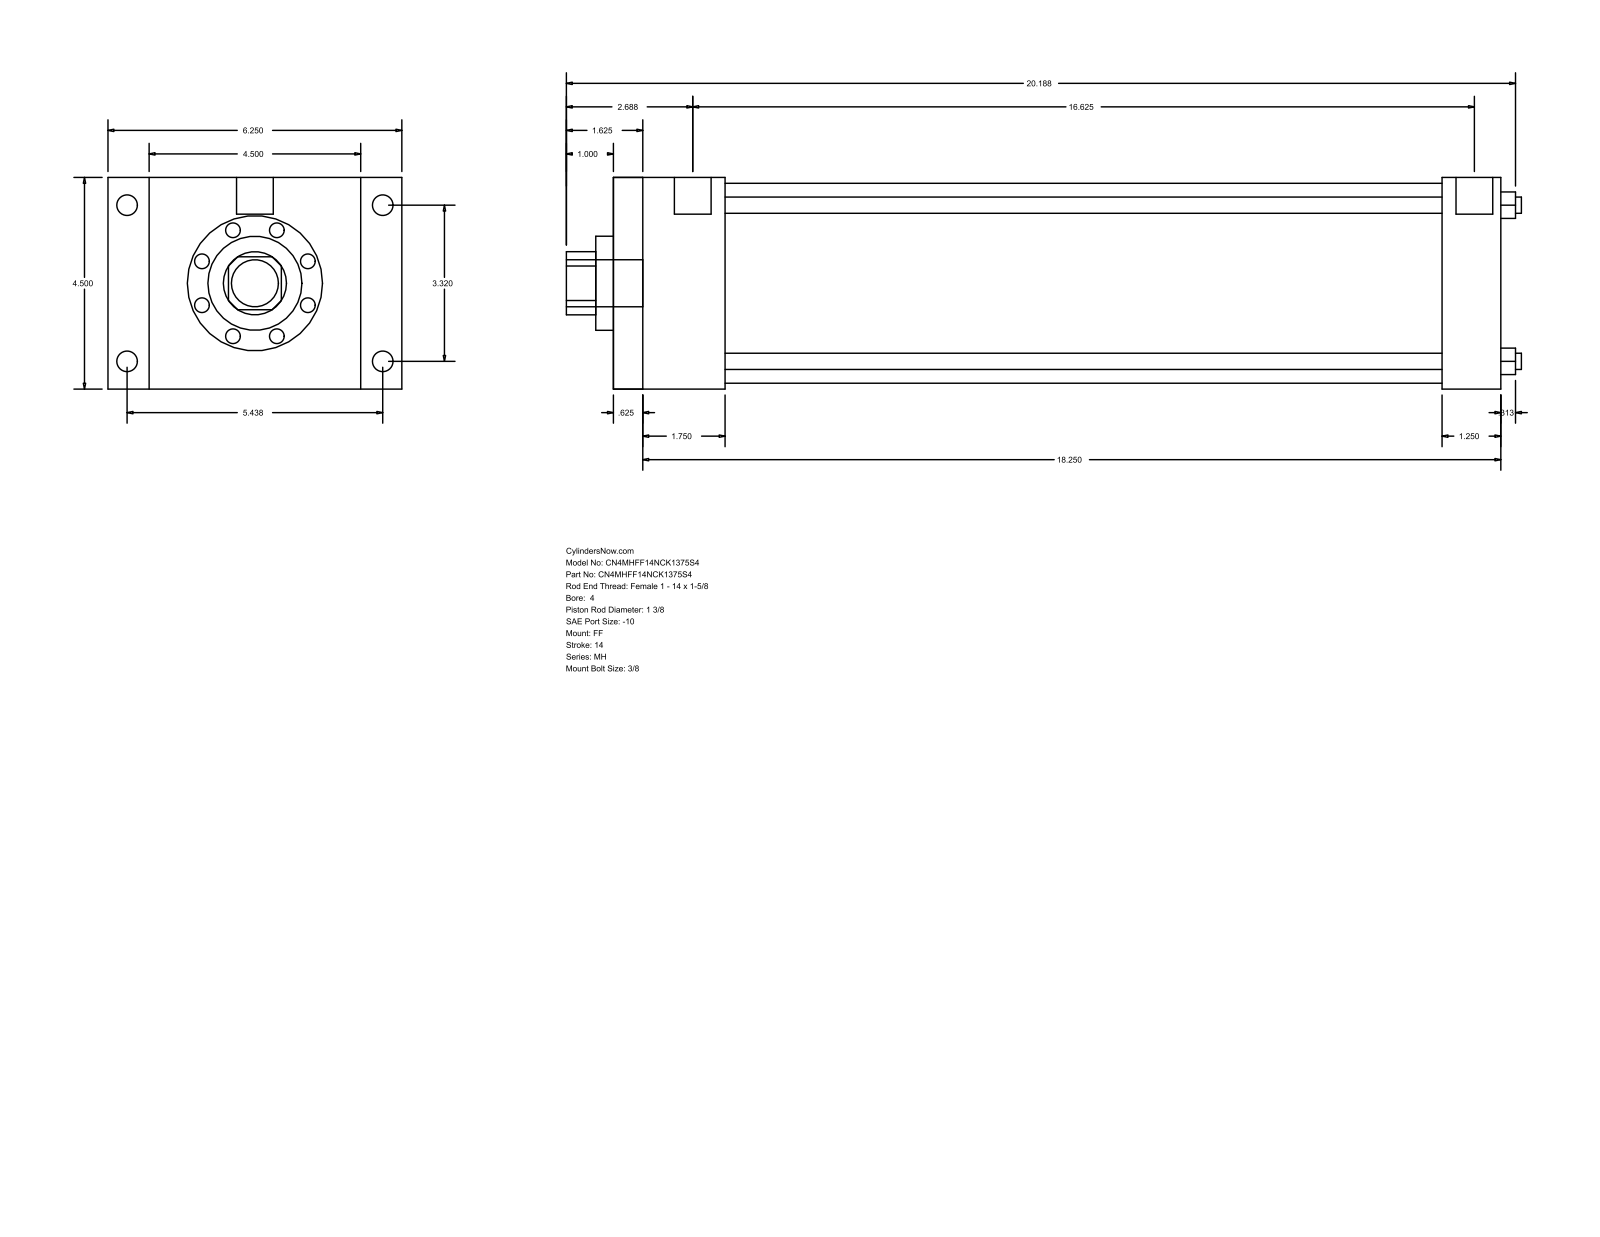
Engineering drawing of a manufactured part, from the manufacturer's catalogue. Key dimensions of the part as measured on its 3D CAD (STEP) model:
Part name (STEP PRODUCT): MH_FF__0400_1.375
STEP written by: GSSL Pune (CONFIG_CONTROL_DESIGN)
Units: millimetres
Bodies: 0 solids, 92 faces (64 planar, 28 cylindrical, 0 other)
Overall size (bounding box): 515.94 × 158.75 × 114.3
Round holes (diameter × count): ⌀8.76 ×4, ⌀34.92 ×1, ⌀50.8 ×1, ⌀107.95 ×1
Round bosses / shafts (diameter × count): ⌀11.13 ×4, ⌀8.73 ×4, ⌀19.84 ×2, ⌀25.4 ×1
Partial cylindrical surfaces — rounded edges, fillets, slot ends (radius × count): R17.06 ×1
Main face-to-face distances: 114.3, 479.42, 15.87, 463.55, 60.32, 44.45, 419.1, 447.67, 431.8, 387.35
Hole centre spacings: 59.62, 84.32, 119.25
